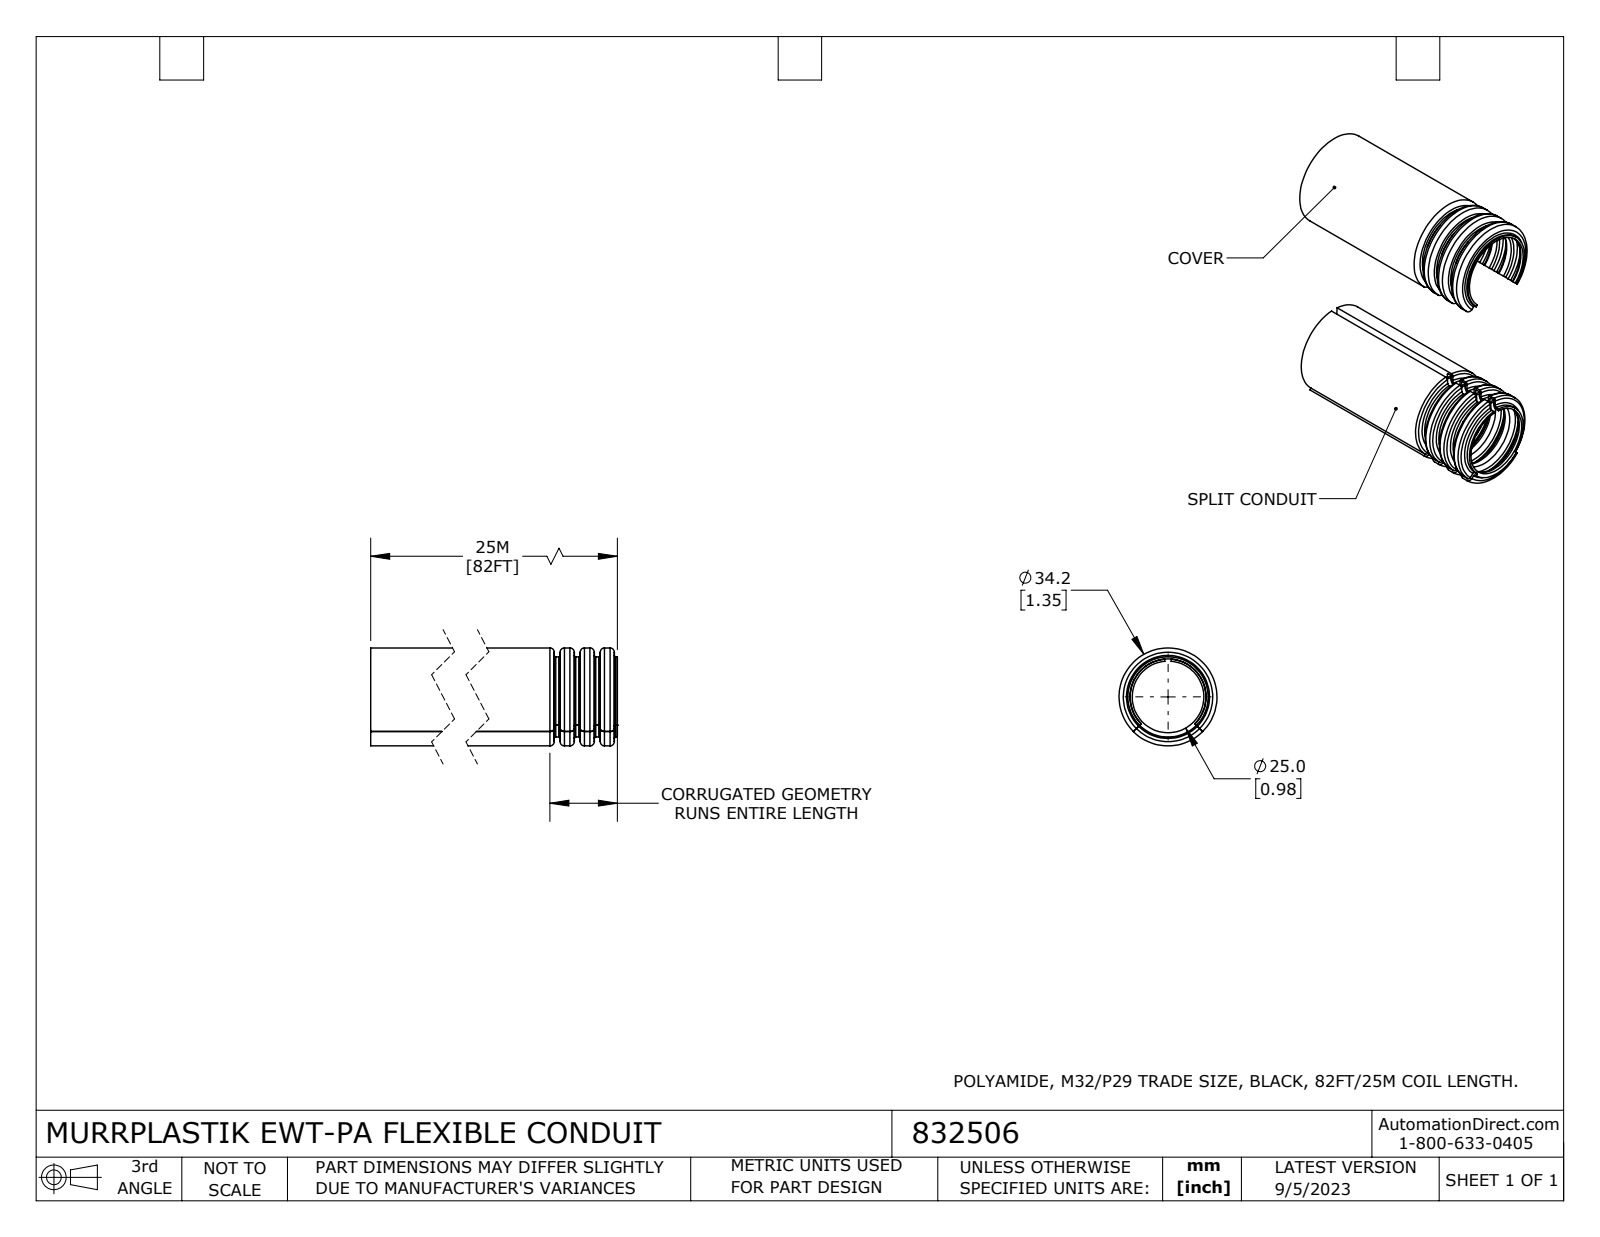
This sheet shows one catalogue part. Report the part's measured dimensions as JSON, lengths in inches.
{"part_name": "832506", "step_written_by": "SolidWorks 2021 (CONFIG_CONTROL_DESIGN)", "units": "inches", "bodies": {"solids": 2, "faces": 341, "planar": 10, "cylindrical": 107, "other": 224}, "overall_size": [3.15, 1.346, 1.346], "volume_in3": 1.752, "surface_area_in2": 51.6, "round_holes": [[0.984, 1], [1.228, 1]], "round_bosses_or_shafts": [[1.346, 1], [1.102, 1]], "partial_cylinders_radius": [[0.522, 1], [0.644, 1]], "face_to_face_distances": [3.15]}
